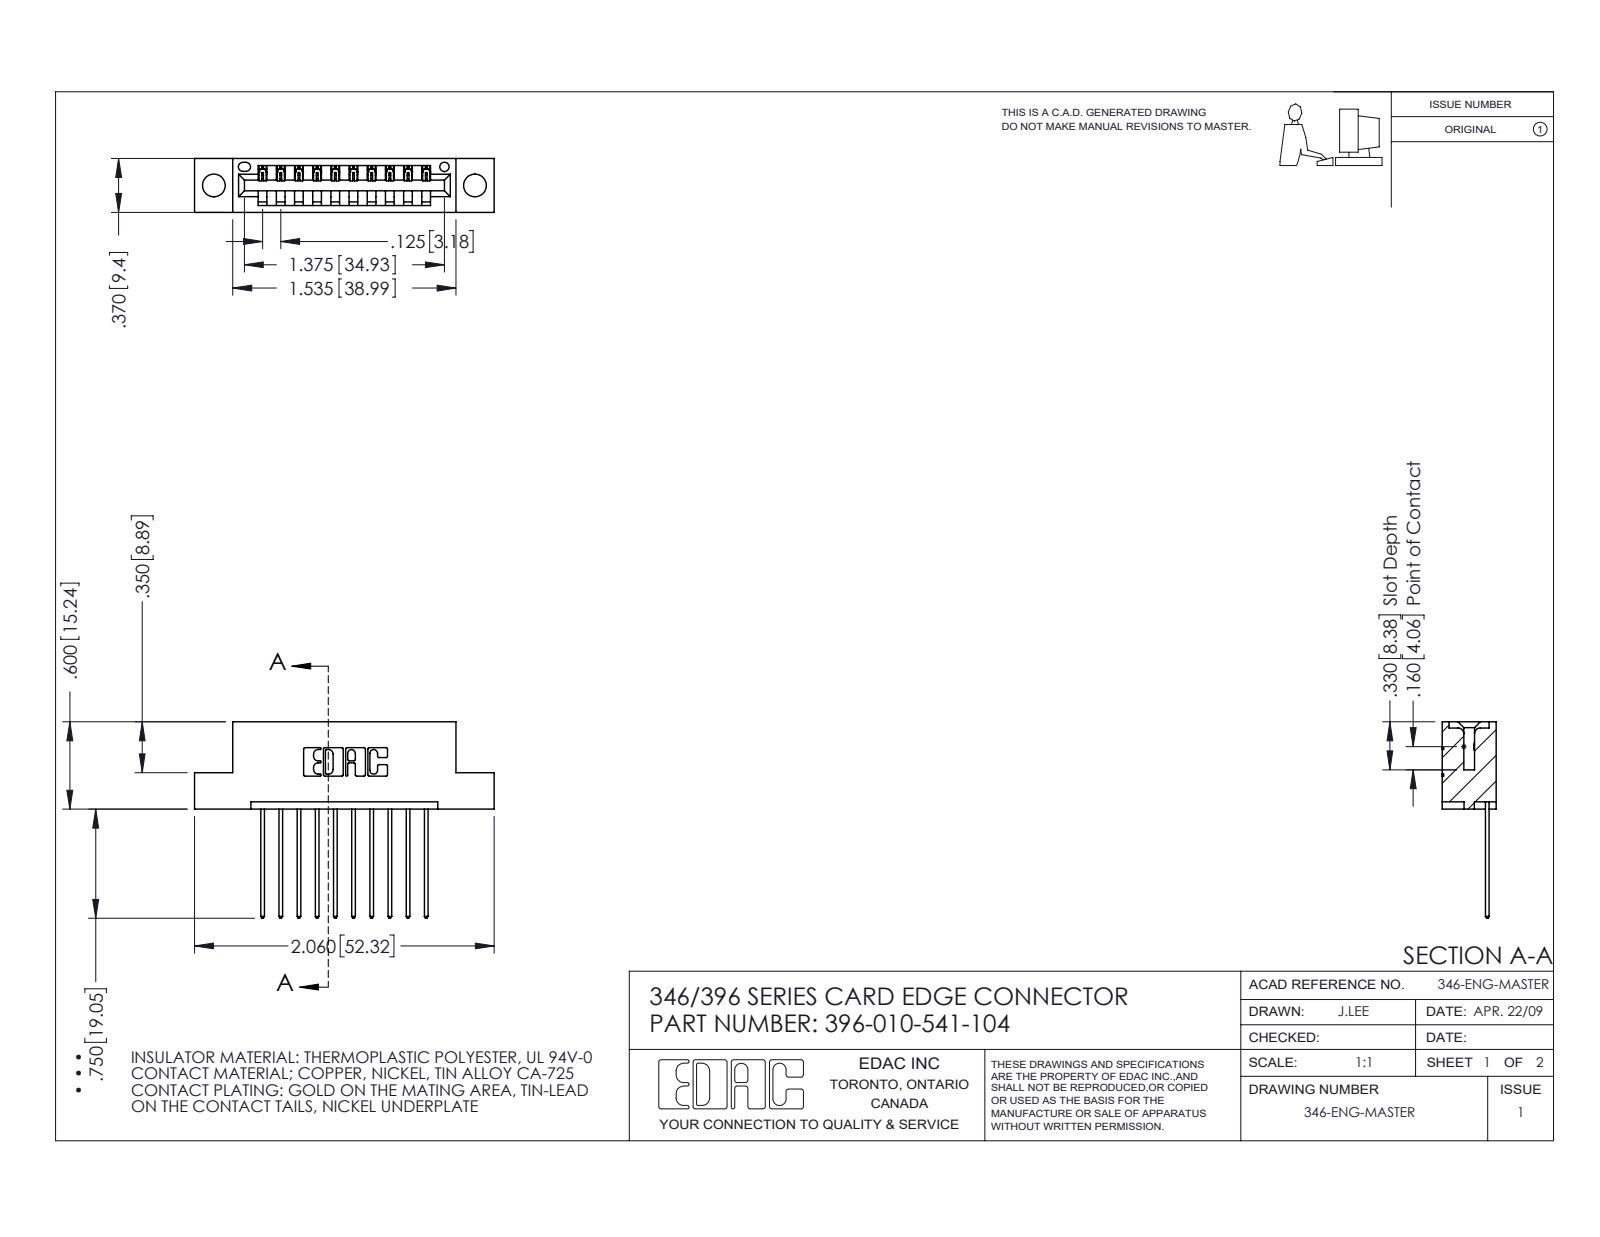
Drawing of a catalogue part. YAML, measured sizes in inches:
part_name: "345-292-001_345-293-141; 346 Part_Flush Mounting Lugs - 0.156 Dia-TH; 396-010-541-104"
step_written_by: "SolidWorks 2016 (CONFIG_CONTROL_DESIGN)"
units: inches
bodies: {solids: 11, faces: 702, planar: 476, cylindrical: 226, other: 0}
overall_size: [2.06, 1.35, 0.37]
volume: 0.289
surface_area: 8.638
round_holes:
  - {diameter: 0.156, count: 2}
  - {diameter: 0.064, count: 1}
partial_cylinders:
  - {radius: 0.01, count: 22}
  - {radius: 0.006, count: 20}
  - {radius: 0.01, count: 20}
  - {radius: 0.007, count: 6}
  - {radius: 0.031, count: 6}
  - {radius: 0.026, count: 3}
  - {radius: 0.031, count: 2}
  - {radius: 0.04, count: 2}
face_to_face_distances: [0.25, 0.048, 0.322, 0.37, 0.072, 0.298, 0.025, 0.148, 0.222, 0.1]
hole_center_spacings: [0.246, 1.59, 1.795]
